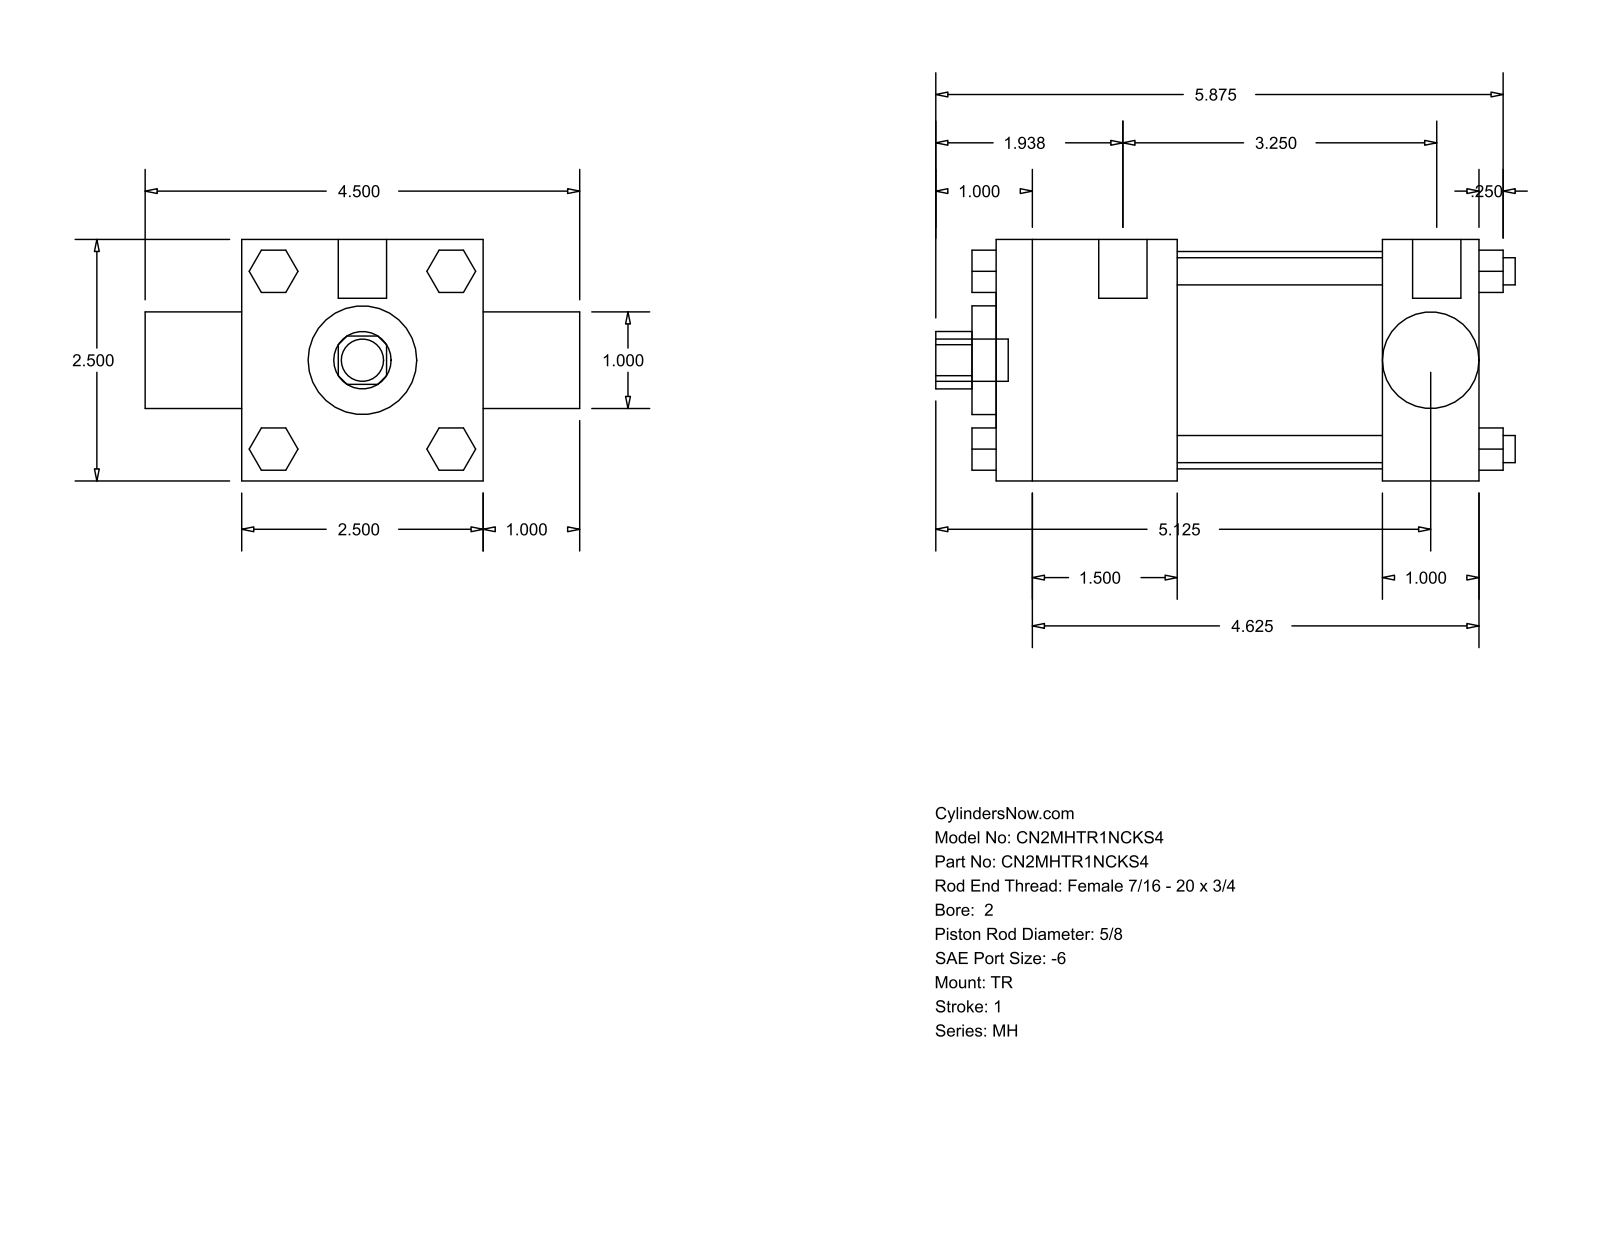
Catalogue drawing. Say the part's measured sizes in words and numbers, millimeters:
The part is named "MH_TR__0200_0.625". Its 3-D file was written by "GSSL Pune (CONFIG_CONTROL_DESIGN)". It is 0 solids with 120 faces: 92 planar, 28 cylindrical and 0 other. Overall it measures 152.4 by 114.3 by 63.5 millimeters. Round holes: 1 of diameter 15.88, 1 of diameter 25.35, 1 of diameter 28.57, 1 of diameter 57.15. Round bosses or shafts: 4 of diameter 7.14, 3 of diameter 5.56, 2 of diameter 12.7, 1 of diameter 11.11. Partial cylindrical surfaces (rounded edges, fillets, slot ends): 1 of radius 7.54. The main face-to-face distances are 63.5, 127, 53.97, 47.62, 101.59, 79.38, 25.41, 25.4, 88.9, 133.35.
